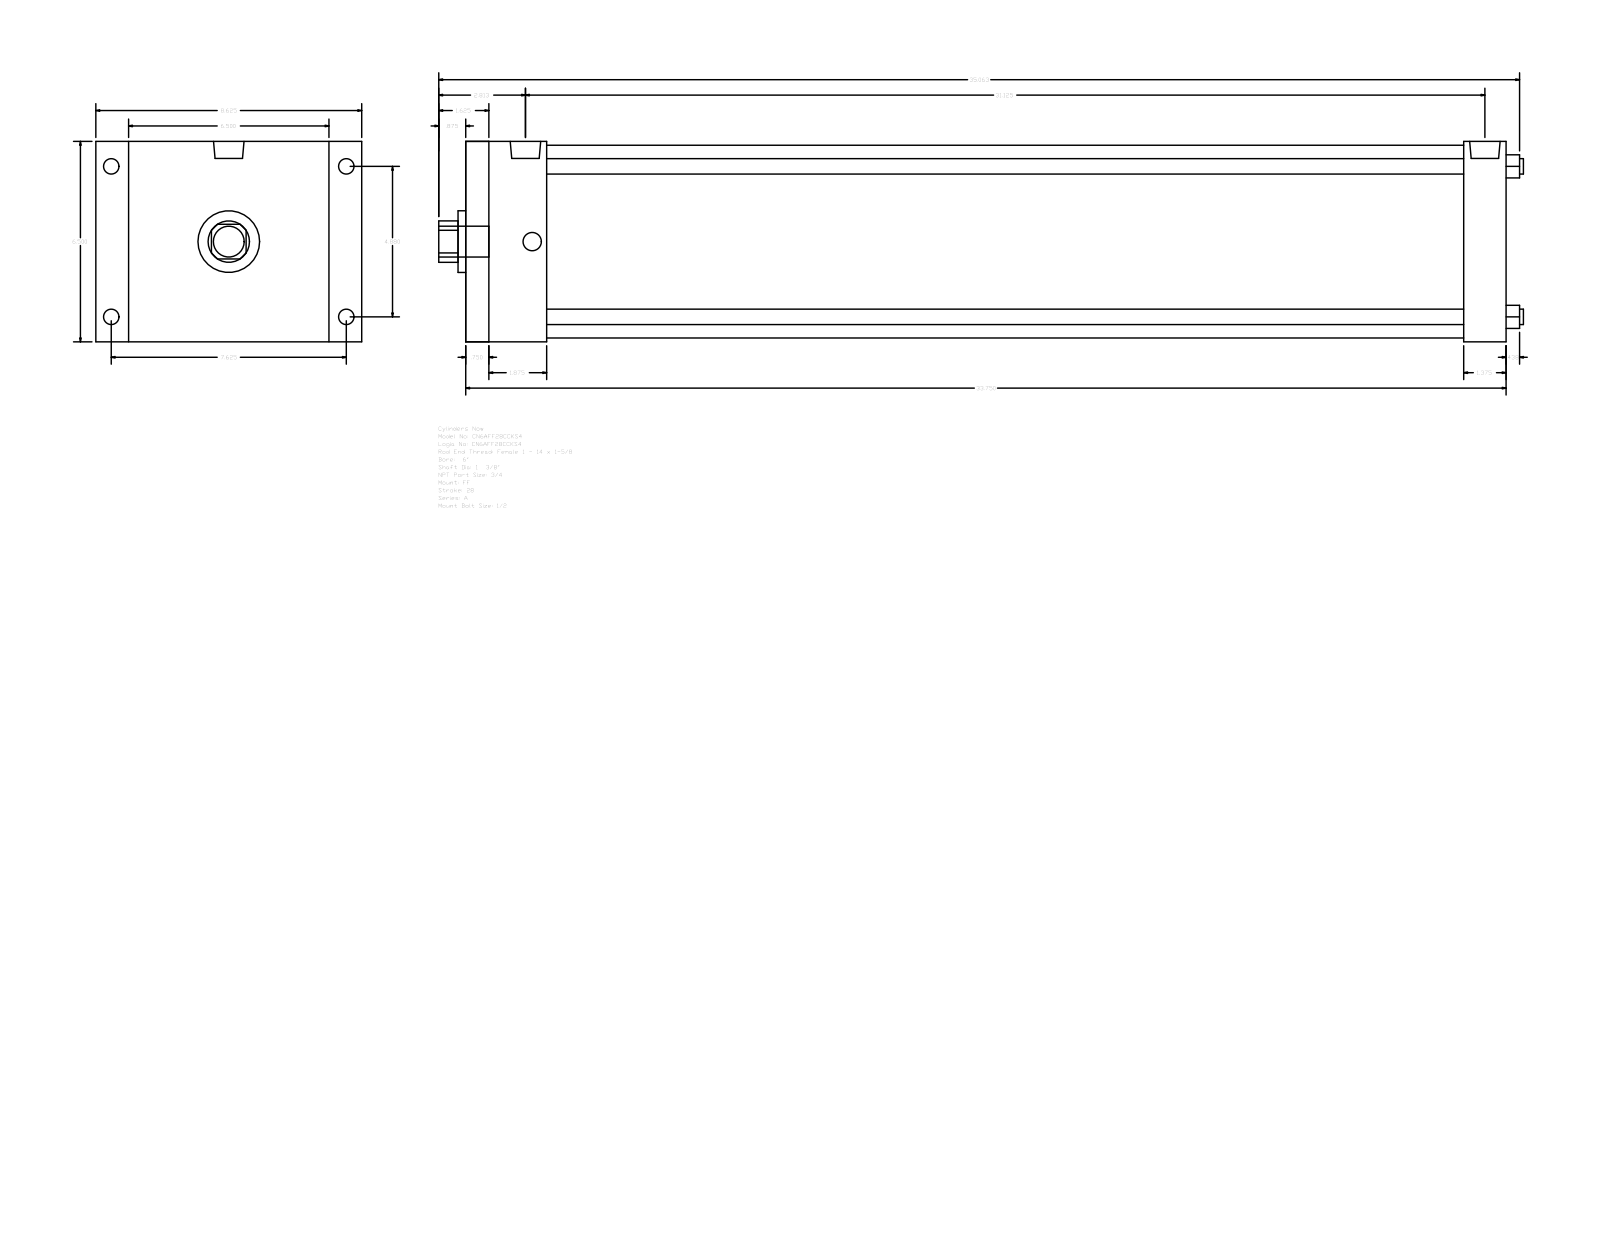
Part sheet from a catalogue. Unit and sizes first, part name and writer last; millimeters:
Units: millimetres
Overall size (bounding box): 893.76 × 219.07 × 165.1
Round holes (diameter × count): ⌀12.7 ×4, ⌀34.92 ×1, ⌀50.8 ×1, ⌀158.75 ×1
Round bosses / shafts (diameter × count): ⌀15.08 ×4, ⌀12.7 ×4, ⌀25.12 ×2, ⌀25.4 ×1
Partial cylindrical surfaces — rounded edges, fillets, slot ends (radius × count): R17.06 ×1
Main face-to-face distances: 165.1, 857.25, 19.04, 838.21, 66.67, 47.63, 790.58, 822.32, 803.28, 755.65
Hole centre spacings: 87.65, 123.96, 175.31
Bodies: 0 solids, 92 faces (64 planar, 28 cylindrical, 0 other)
Part name (STEP PRODUCT): A_FF__0600_1.375
STEP written by: GSSL Pune (CONFIG_CONTROL_DESIGN)
